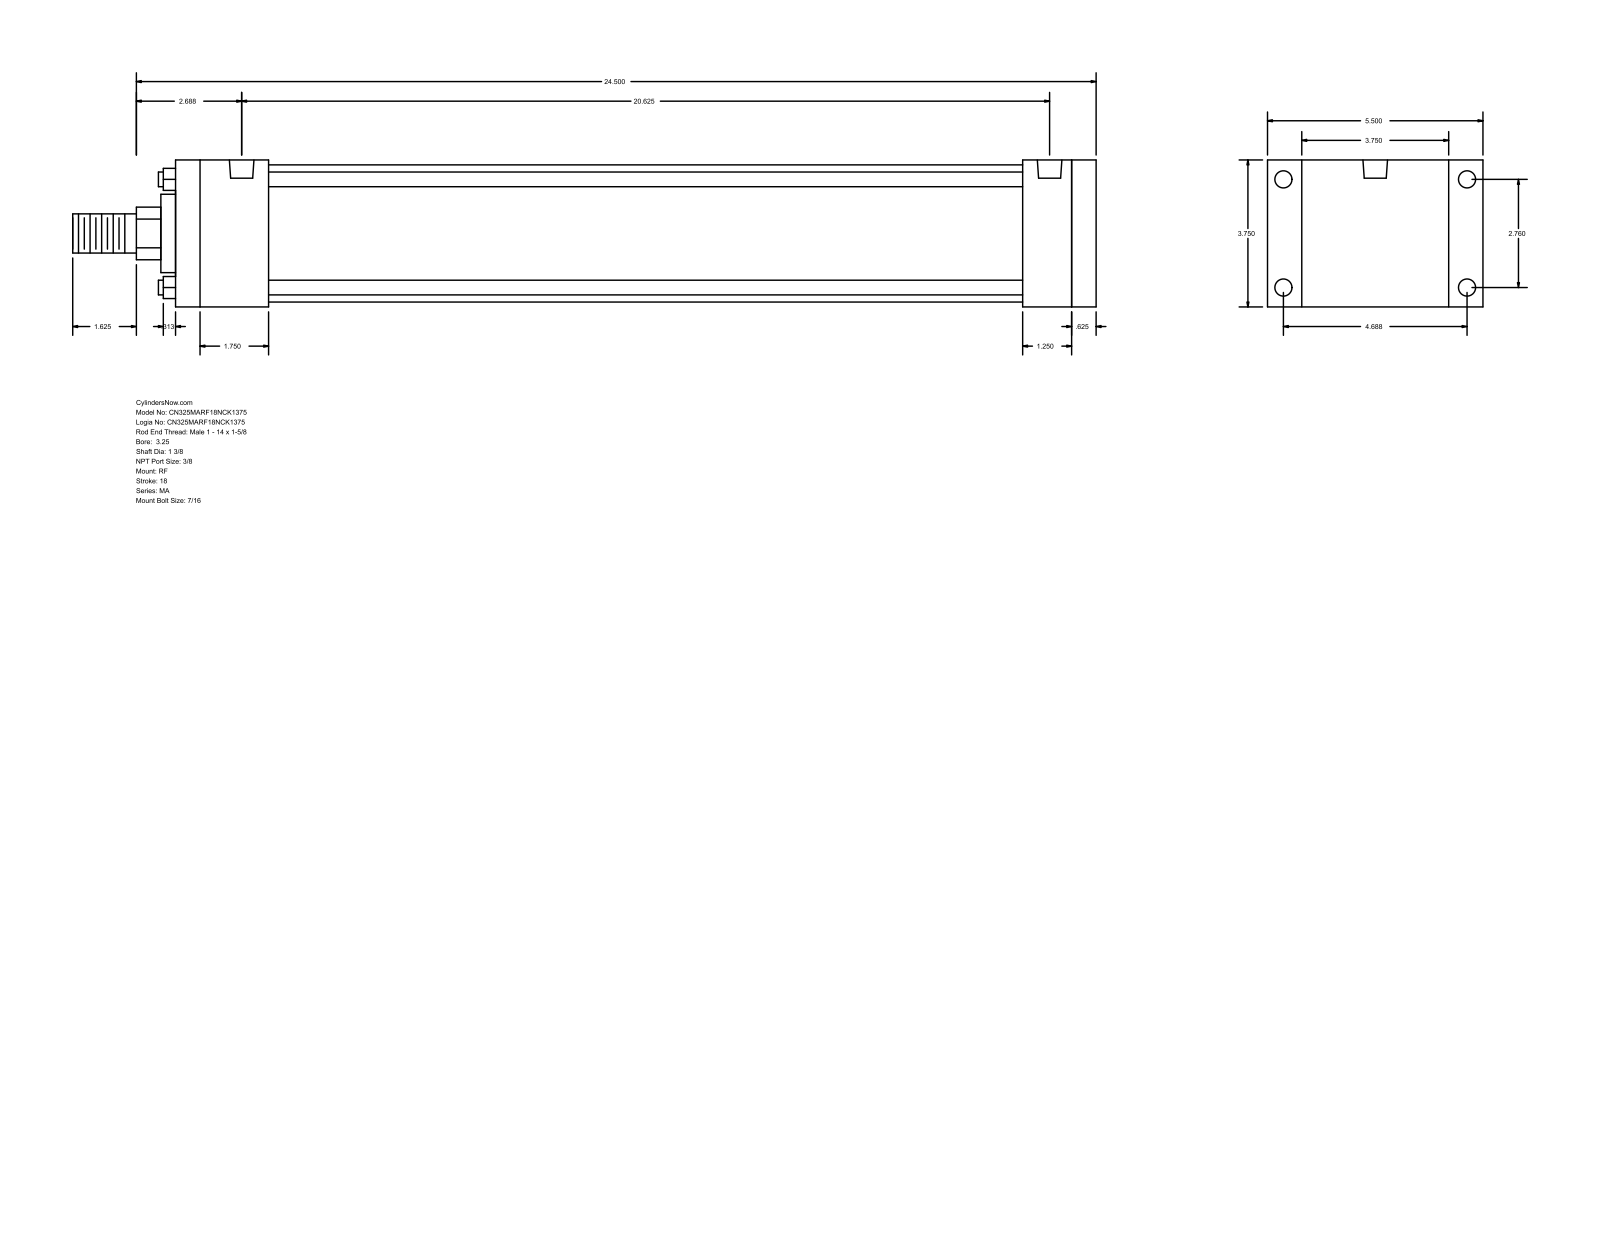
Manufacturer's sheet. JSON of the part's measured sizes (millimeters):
{"part_name": "MA_RF__0325_1.375", "step_written_by": "GSSL Pune (CONFIG_CONTROL_DESIGN)", "units": "millimeters", "bodies": {"solids": 0, "faces": 92, "planar": 64, "cylindrical": 28, "other": 0}, "overall_size": [663.58, 139.7, 95.25], "round_holes": [[11.11, 8], [15.93, 2]], "round_bosses_or_shafts": [[9.53, 4], [88.9, 1], [50.8, 1], [34.92, 1], [25.4, 1]], "partial_cylinders_radius": [[17.06, 1]], "face_to_face_distances": [95.24, 596.9, 15.88, 581.02, 22.23, 117.47, 549.27, 31.75, 47.63, 60.32], "hole_center_spacings": [70.1, 119.06, 138.16, 514.35, 4.76, 4.77, 519.11, 519.12]}
